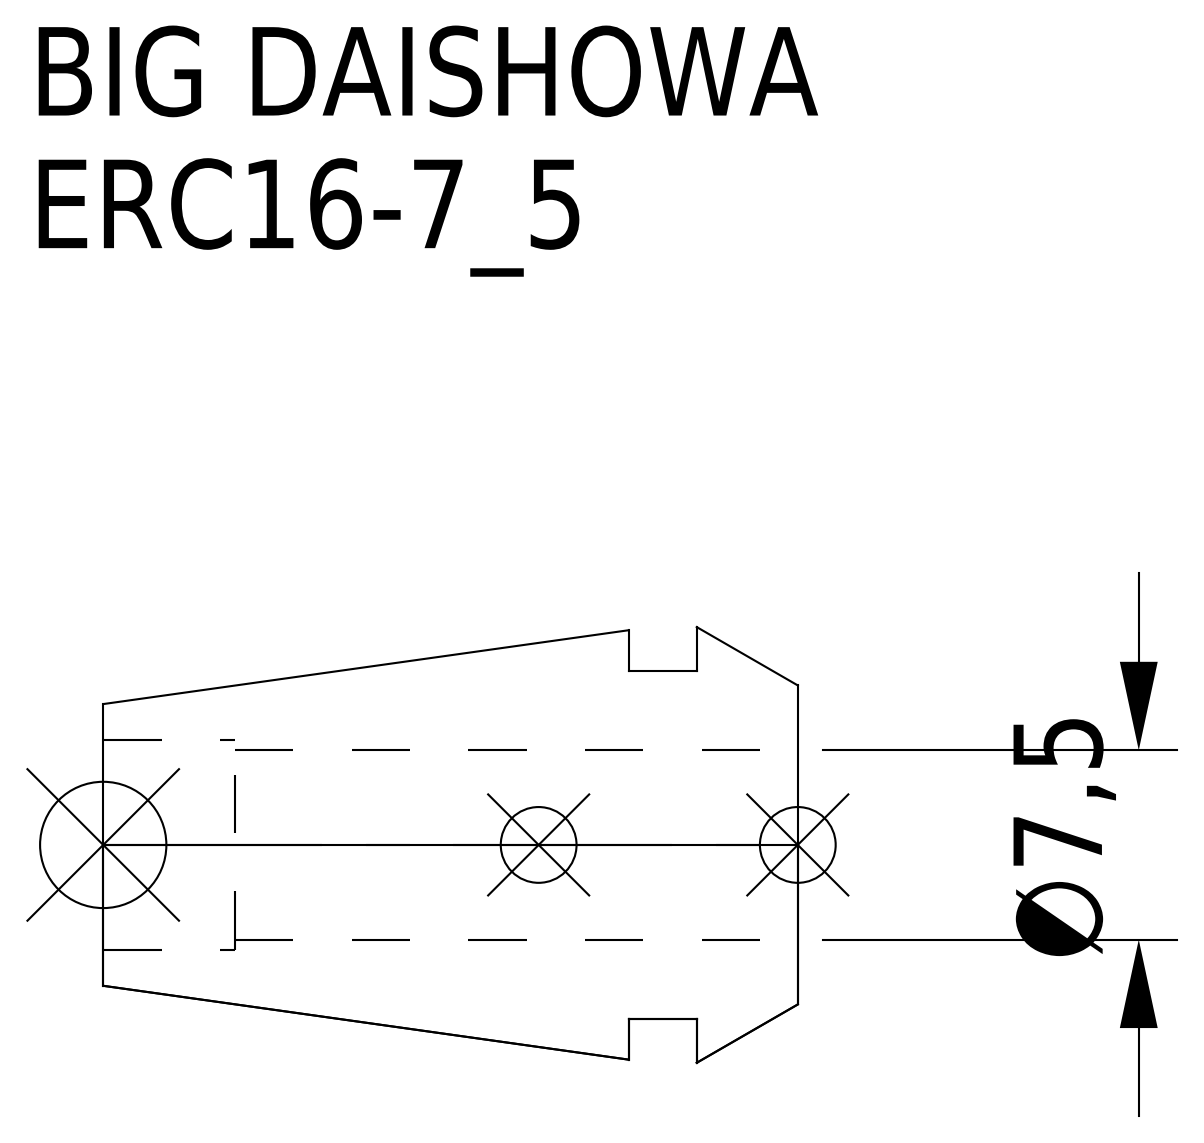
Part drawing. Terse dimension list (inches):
name: ERC16-7_5
written by: CREO PARAMETRIC BY PTC INC, 2016380 (AUTOMOTIVE_DESIGN)
unit: in
bodies: 1 solid, 15 faces (5 planar, 6 cylindrical, 4 other)
size: 1.083 × 0.679 × 0.679
volume: 0.191 in³; area: 3.441 in²
holes: 1× ⌀0.295, 1× ⌀0.327
bosses: 1× ⌀0.543
face distances: 0.157, 0.264, 0.106, 1.083, 0.925, 0.819, 0.878, 0.72, 0.614, 0.205
